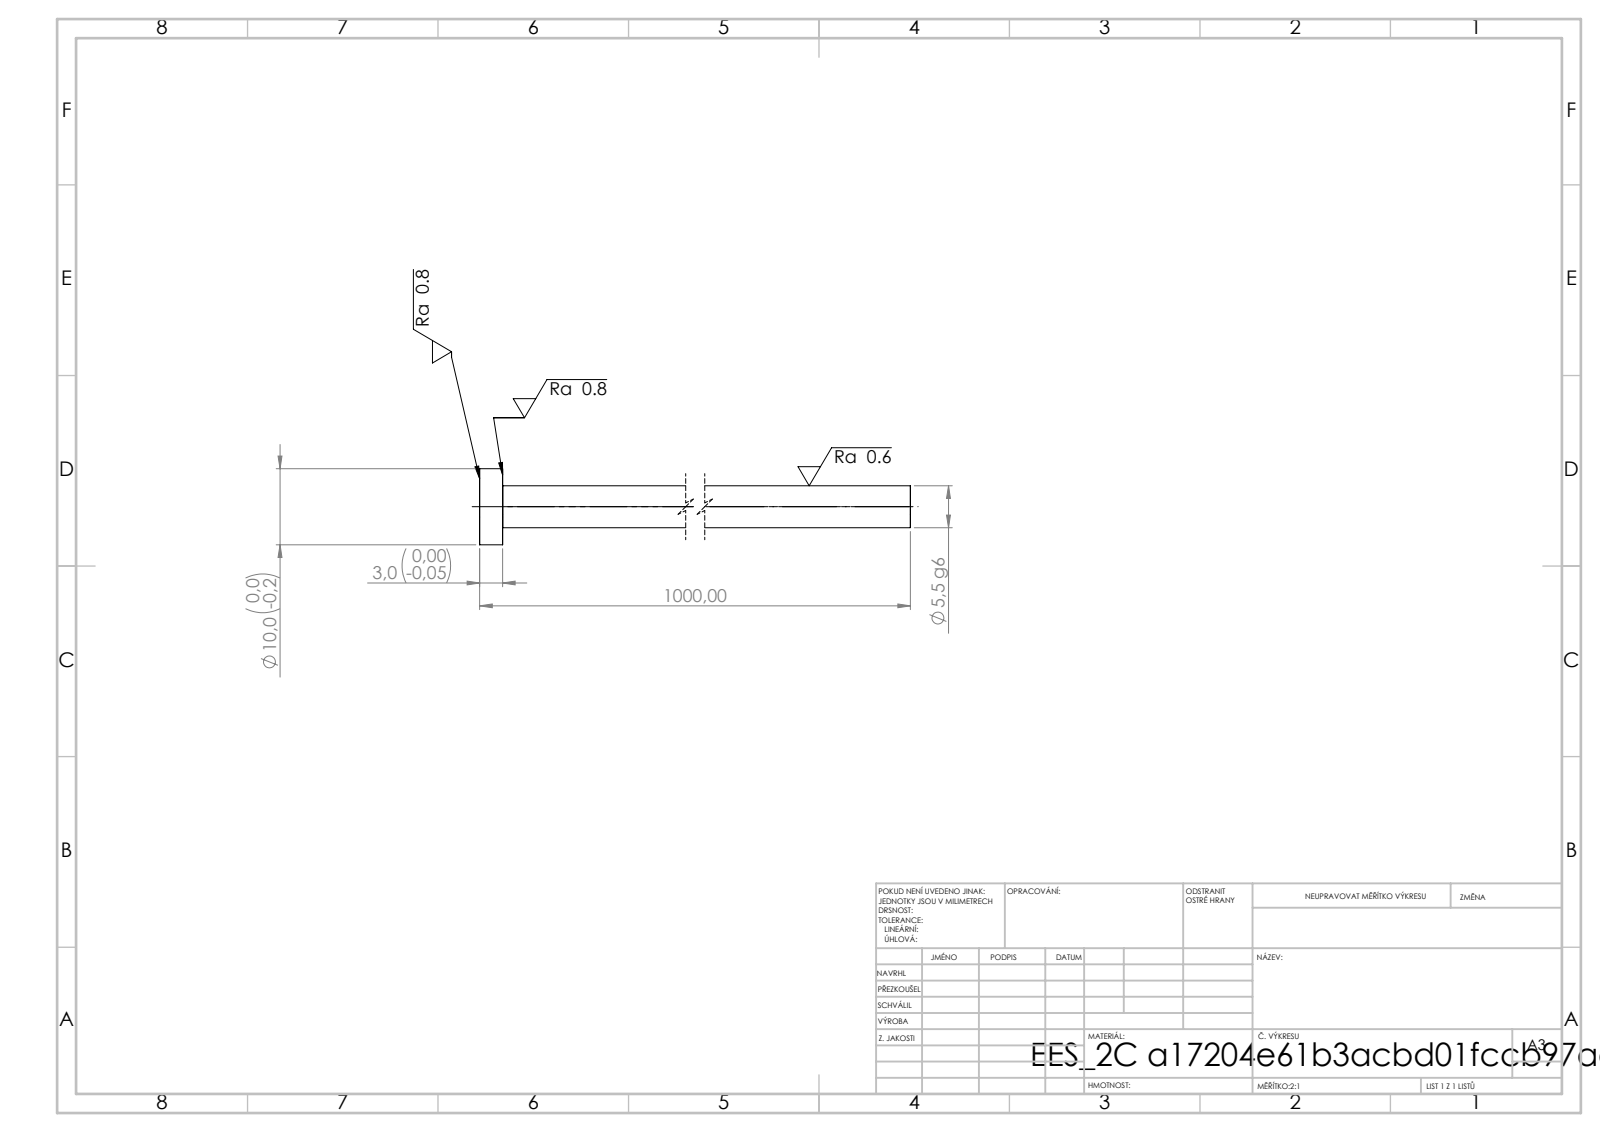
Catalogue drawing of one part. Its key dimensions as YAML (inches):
step_written_by: "SolidWorks 2019 (CONFIG_CONTROL_DESIGN)"
units: inches
bodies: {solids: 1, faces: 7, planar: 3, cylindrical: 4, other: 0}
overall_size: [39.37, 0.394, 0.394]
volume: 1.46
surface_area: 27.09
round_bosses_or_shafts:
  - {diameter: 0.394, count: 1}
  - {diameter: 0.217, count: 1}
face_to_face_distances: [0.118, 39.37, 39.252]
